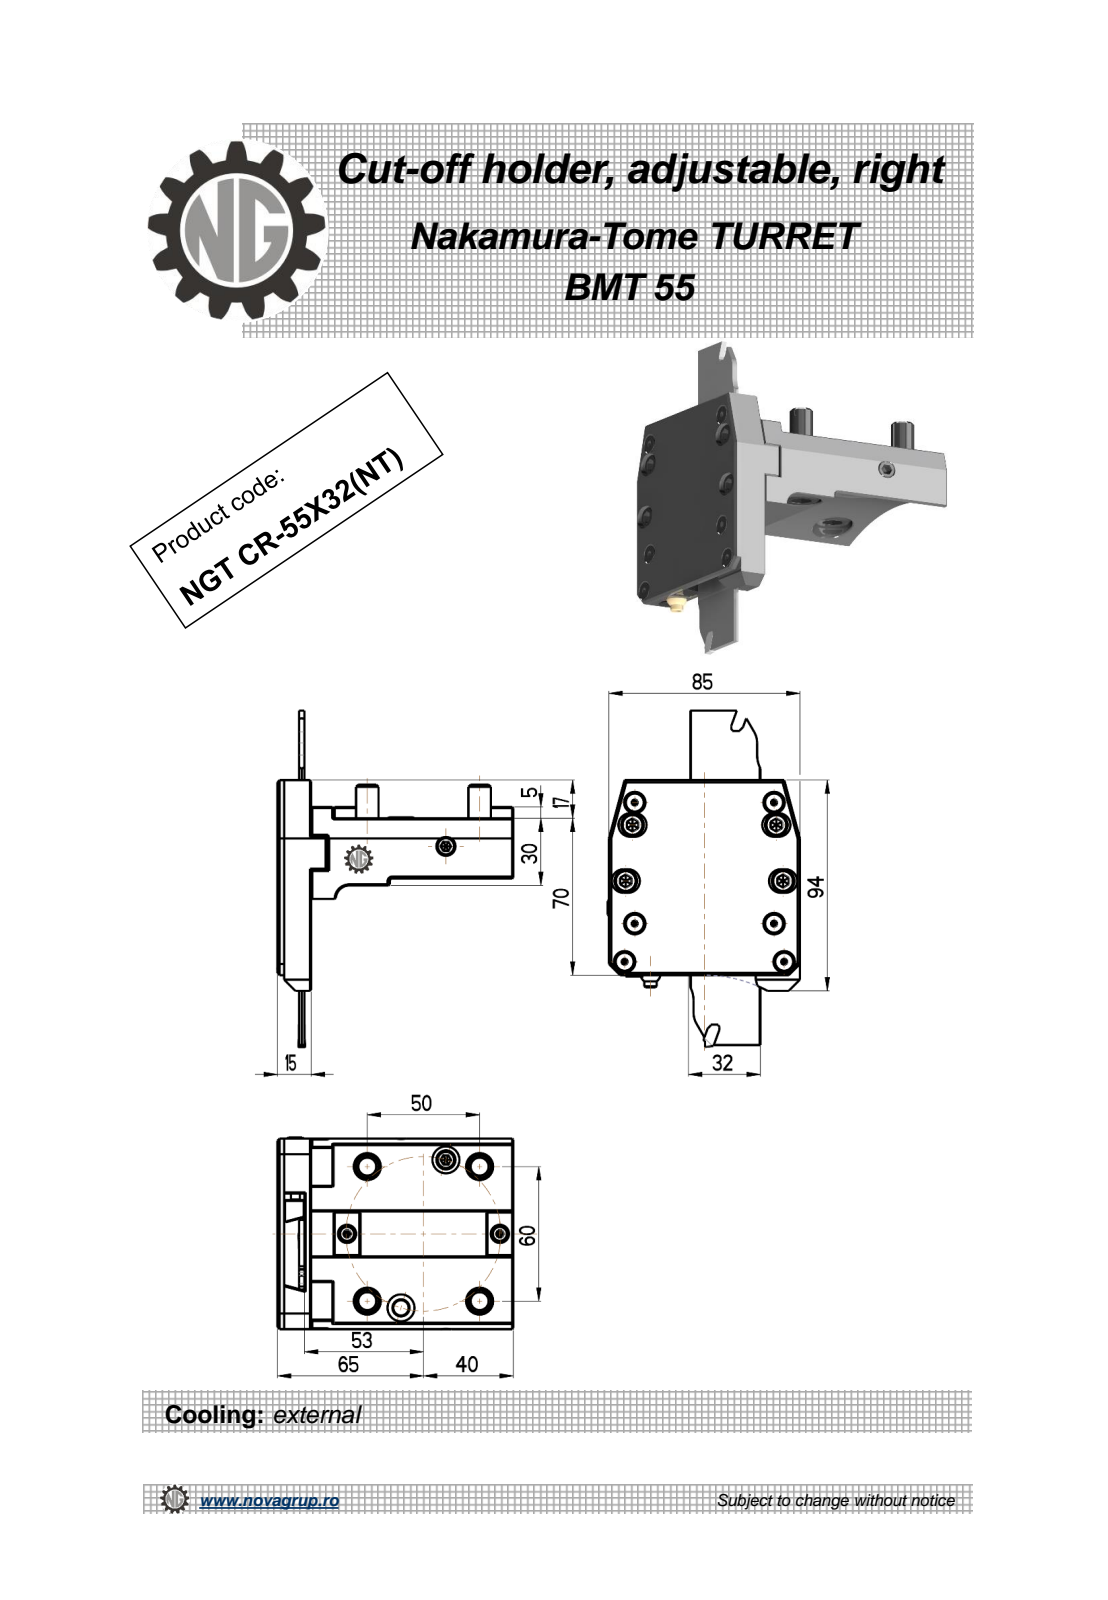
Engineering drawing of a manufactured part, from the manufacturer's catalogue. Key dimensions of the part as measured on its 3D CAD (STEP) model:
Part name (STEP PRODUCT): NGT_CR_55_32_NT
STEP written by: PRO/ENGINEER BY PARAMETRIC TECHNOLOGY CORPORATION, 2010280 (CONFIG_CONTROL_DESIGN)
Units: millimetres
Bodies: 1 solid, 540 faces (302 planar, 136 cylindrical, 102 other)
Overall size (bounding box): 105 × 94 × 85.53
Volume: 262 875 mm³ · Surface area: 62 175 mm²
Round holes (diameter × count): ⌀8 ×4, ⌀5 ×3, ⌀12 ×2, ⌀3.5 ×1, ⌀4.5 ×1, ⌀6.8 ×1, ⌀9 ×1
Round bosses / shafts (diameter × count): ⌀10 ×8, ⌀4 ×4, ⌀6 ×2, ⌀8 ×1, ⌀7 ×1, ⌀5.5 ×1
Partial cylindrical surfaces — rounded edges, fillets, slot ends (radius × count): R0.2 ×24, R0.31 ×12, R5.25 ×8, R0.14 ×6, R0.16 ×6, R0.41 ×6, R1 ×1, R6 ×1
Main face-to-face distances: 12, 3, 15, 9, 25, 85, 5, 10, 22, 90
Hole centre spacings: 17, 24.5, 41.5, 66.12, 68.96, 72.93
